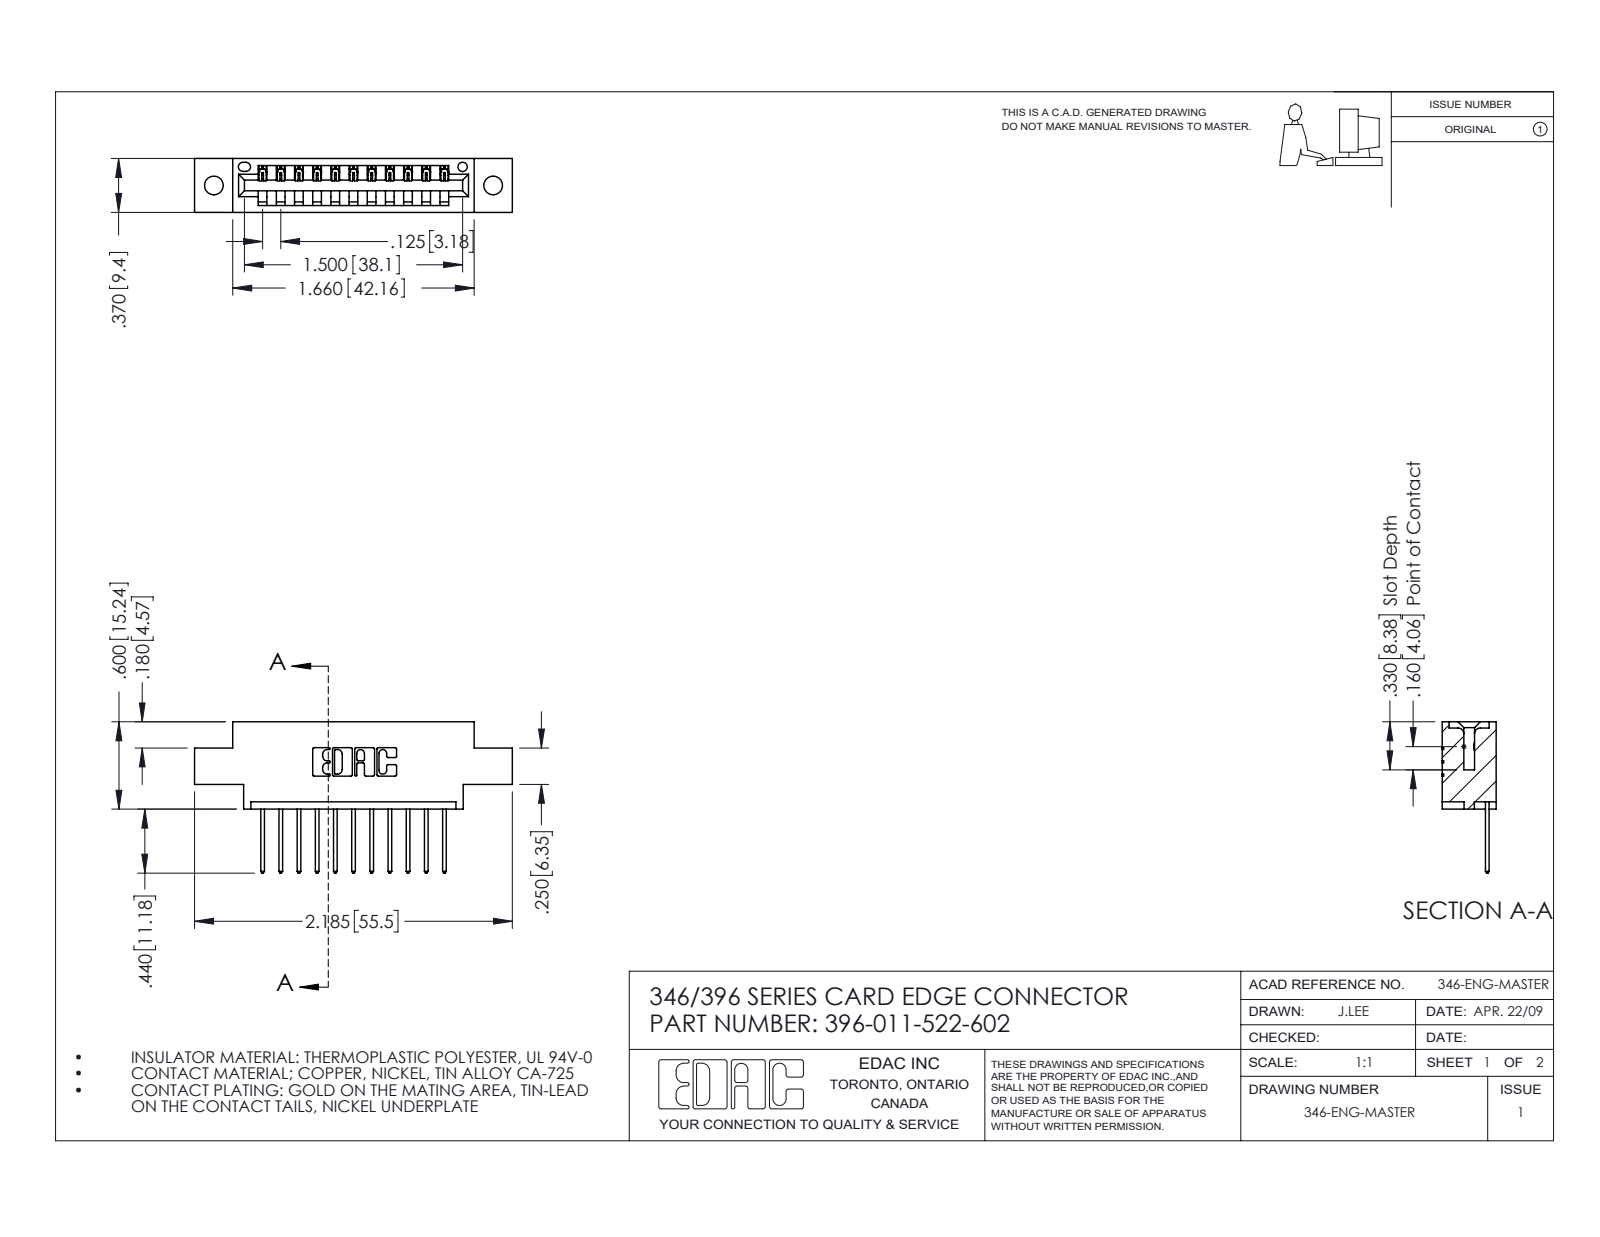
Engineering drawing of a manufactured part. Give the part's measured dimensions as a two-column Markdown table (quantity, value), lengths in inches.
| quantity | value |
| --- | --- |
| part name | 396-011-522-602; 345-292-001_345-293-122; 346 Part_0.170 Offset - 0.128 Dia |
| STEP written by | SolidWorks 2016 (CONFIG_CONTROL_DESIGN) |
| units | inches |
| bodies | 12 solids, 764 faces (520 planar, 244 cylindrical, 0 other) |
| overall size | 2.185 × 1.04 × 0.37 |
| volume | 0.3 in³ |
| surface area | 8.883 in² |
| round holes (diameter × count) | 0.128 × 2, 0.064 × 1 |
| partial cylindrical surfaces (radius × count) | 0.006 × 22, 0.01 × 22, 0.01 × 22, 0.007 × 6, 0.031 × 6, 0.026 × 3, 0.031 × 2, 0.04 × 2 |
| main face-to-face distances | 0.25, 0.37, 0.048, 0.322, 0.072, 0.298, 0.025, 0.148, 0.222, 0.1 |
| hole center spacings | 0.246, 1.715, 1.92 |
